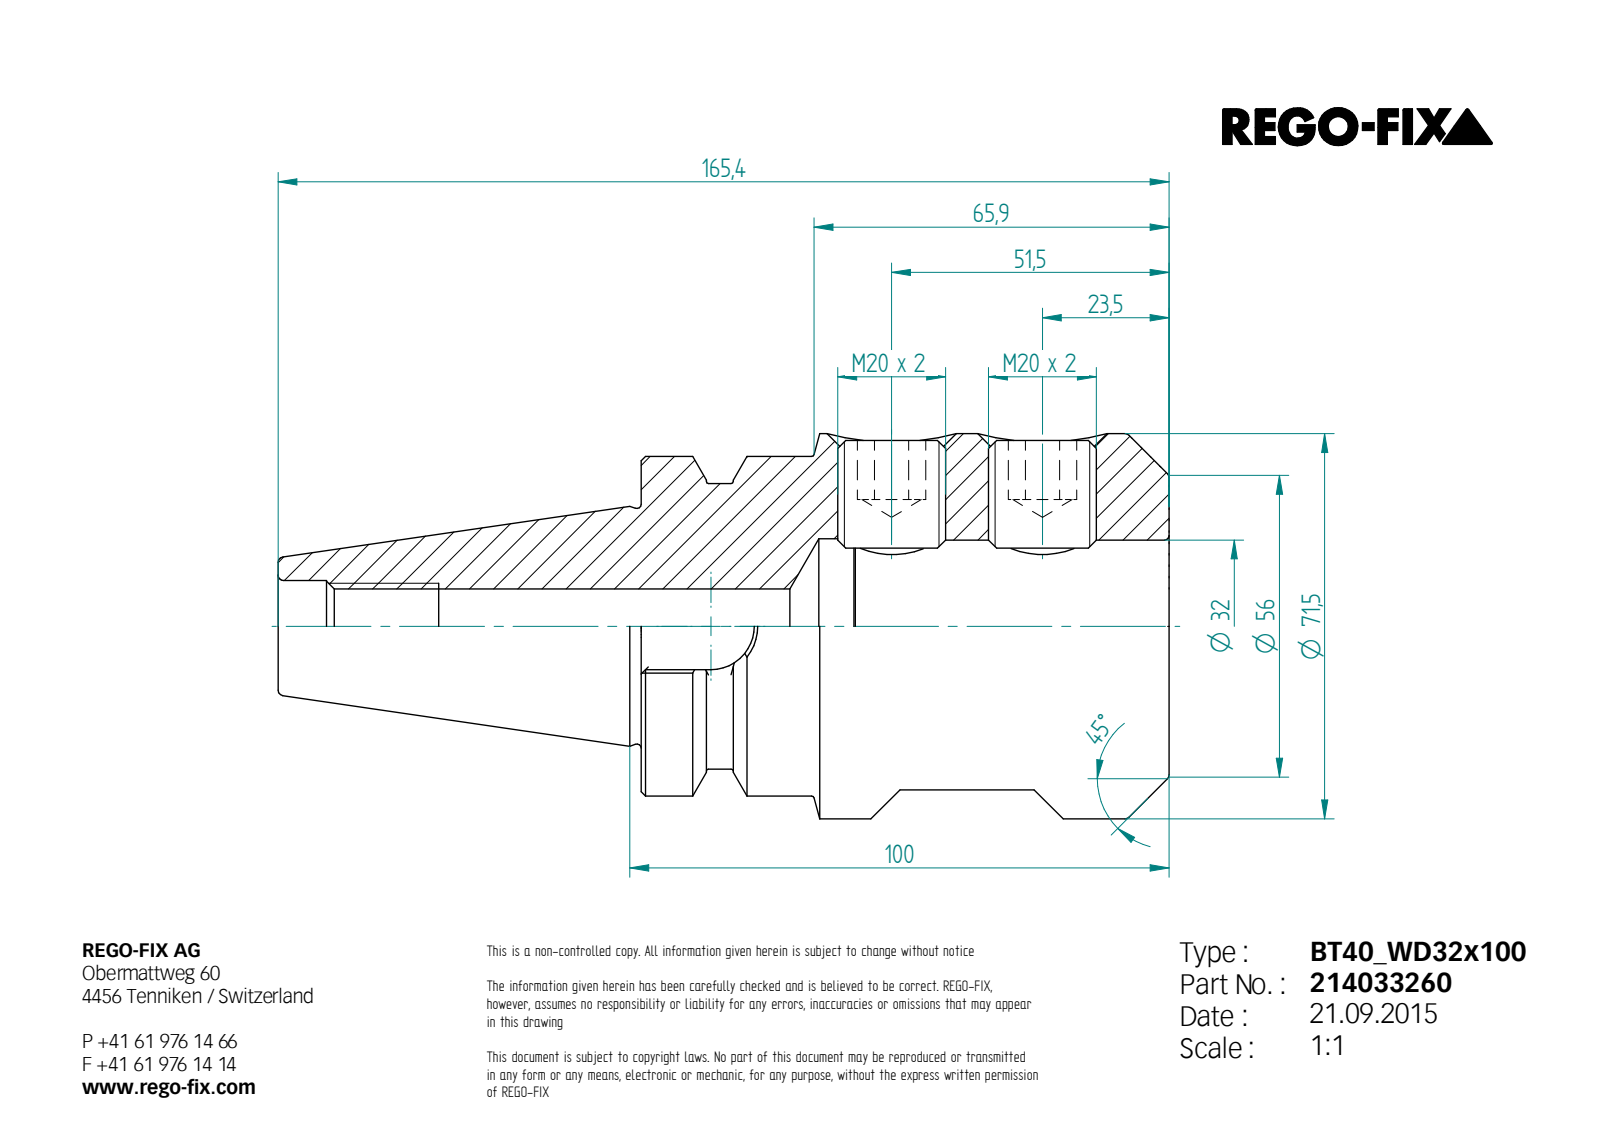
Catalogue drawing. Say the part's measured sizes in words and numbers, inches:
Its 3-D file was written by "Unknown (AUTOMOTIVE_DESIGN)". It is 3 solids with 123 faces: 66 planar, 21 cylindrical and 36 other. Overall it measures 6.512 by 2.815 by 2.815 inches. Its volume is 20.75 cubic inches and its surface area 79.57 square inches. Round holes: 2 of diameter 0.702, 1 of diameter 0.545, 1 of diameter 0.669, 1 of diameter 1.26, 1 of diameter 1.28. Round bosses or shafts: 2 of diameter 0.787, 1 of diameter 2.815, 1 of diameter 2.48, 1 of diameter 2.087. Partial cylindrical surfaces (rounded edges, fillets, slot ends): 4 of radius 0.02, 1 of radius 0.317. The main face-to-face distances are 3.858, 1.766, 0.433, 1.776, 0.671, 1.104, 0.955, 2.553, 0.787, 2.654. The hole center spacings are 1.102.
